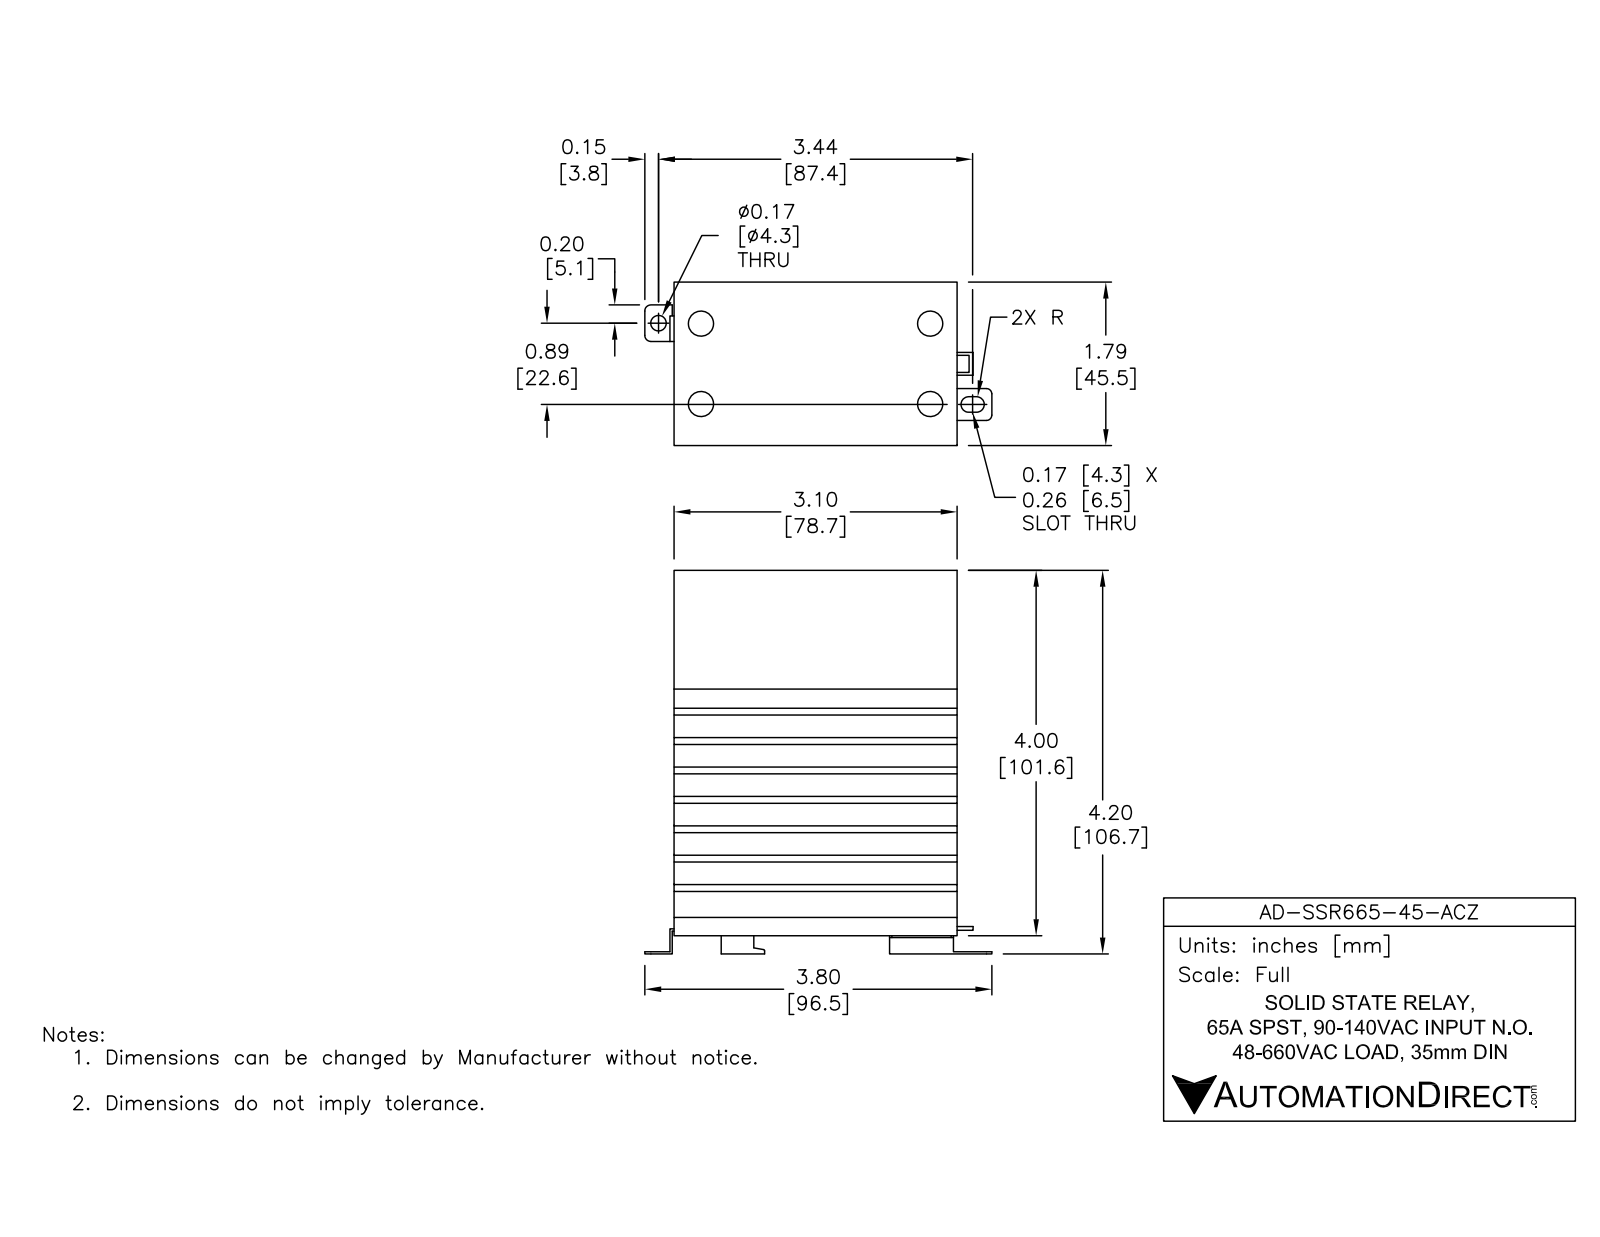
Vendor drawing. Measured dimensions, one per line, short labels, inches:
name: AD-SSR665-45-ACZ
written by: SolidWorks 2014 (AUTOMOTIVE_DESIGN)
unit: in
bodies: 1 solid, 171 faces (151 planar, 20 cylindrical, 0 other)
size: 4.2 × 3.8 × 1.79
volume: 12.46 in³; area: 125.1 in²
holes: 2× ⌀0.275, 2× ⌀0.275, 1× ⌀0.17
rounds: 2× R0.05, 2× R0.058, 2× R0.067, 2× R0.085, 1× R0.015
face distances: 0.644, 0.322, 0.966, 0.397, 0.322, 0.247, 1.609, 0.075, 0.569, 0.075
hole spacings: 0.88, 2.51, 2.66, 0.465, 1, 2.975, 3.104
